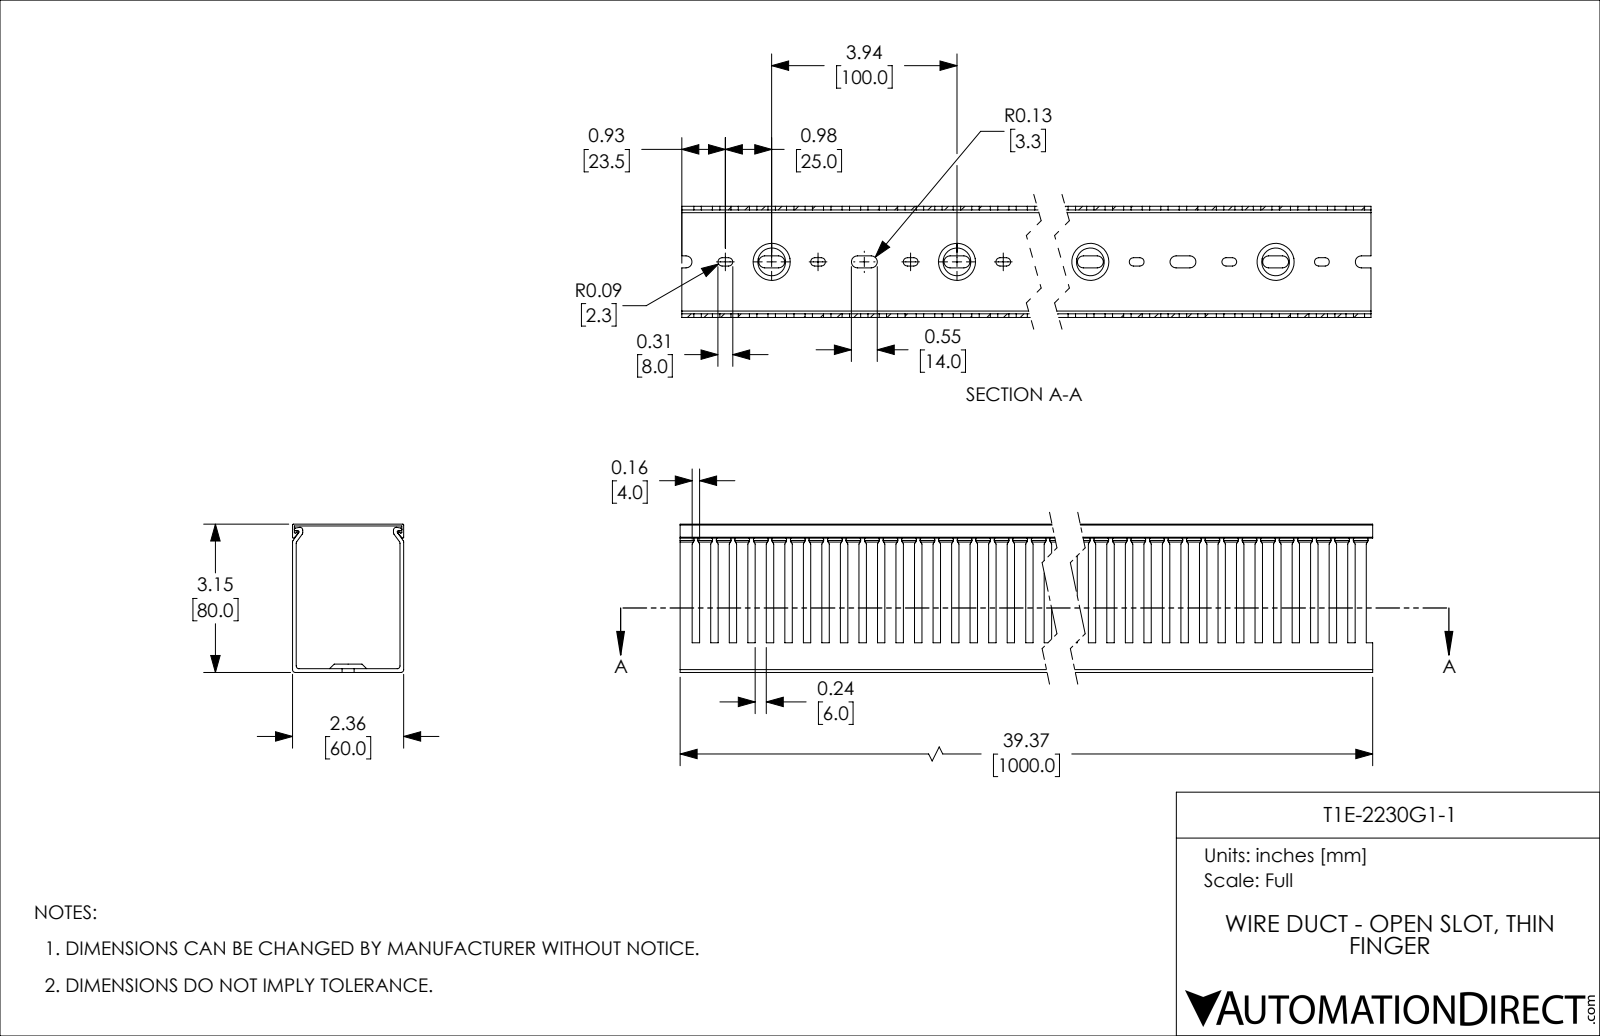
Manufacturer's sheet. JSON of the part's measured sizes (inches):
{"part_name": "T1E-2230G1-1", "step_written_by": "SolidWorks 2021 (CONFIG_CONTROL_DESIGN)", "units": "inches", "bodies": {"solids": 2, "faces": 775, "planar": 444, "cylindrical": 311, "other": 20}, "overall_size": [39.37, 3.15, 2.362], "volume_in3": 30.8, "surface_area_in2": 909.6, "partial_cylinders_radius": [[0.089, 40], [0.128, 40], [0.059, 12], [0.02, 8], [0.03, 6]], "face_to_face_distances": [0.079, 2.283, 2.362, 0.039, 2.205, 3.15, 3.11, 3.031, 3.071, 2.323]}
